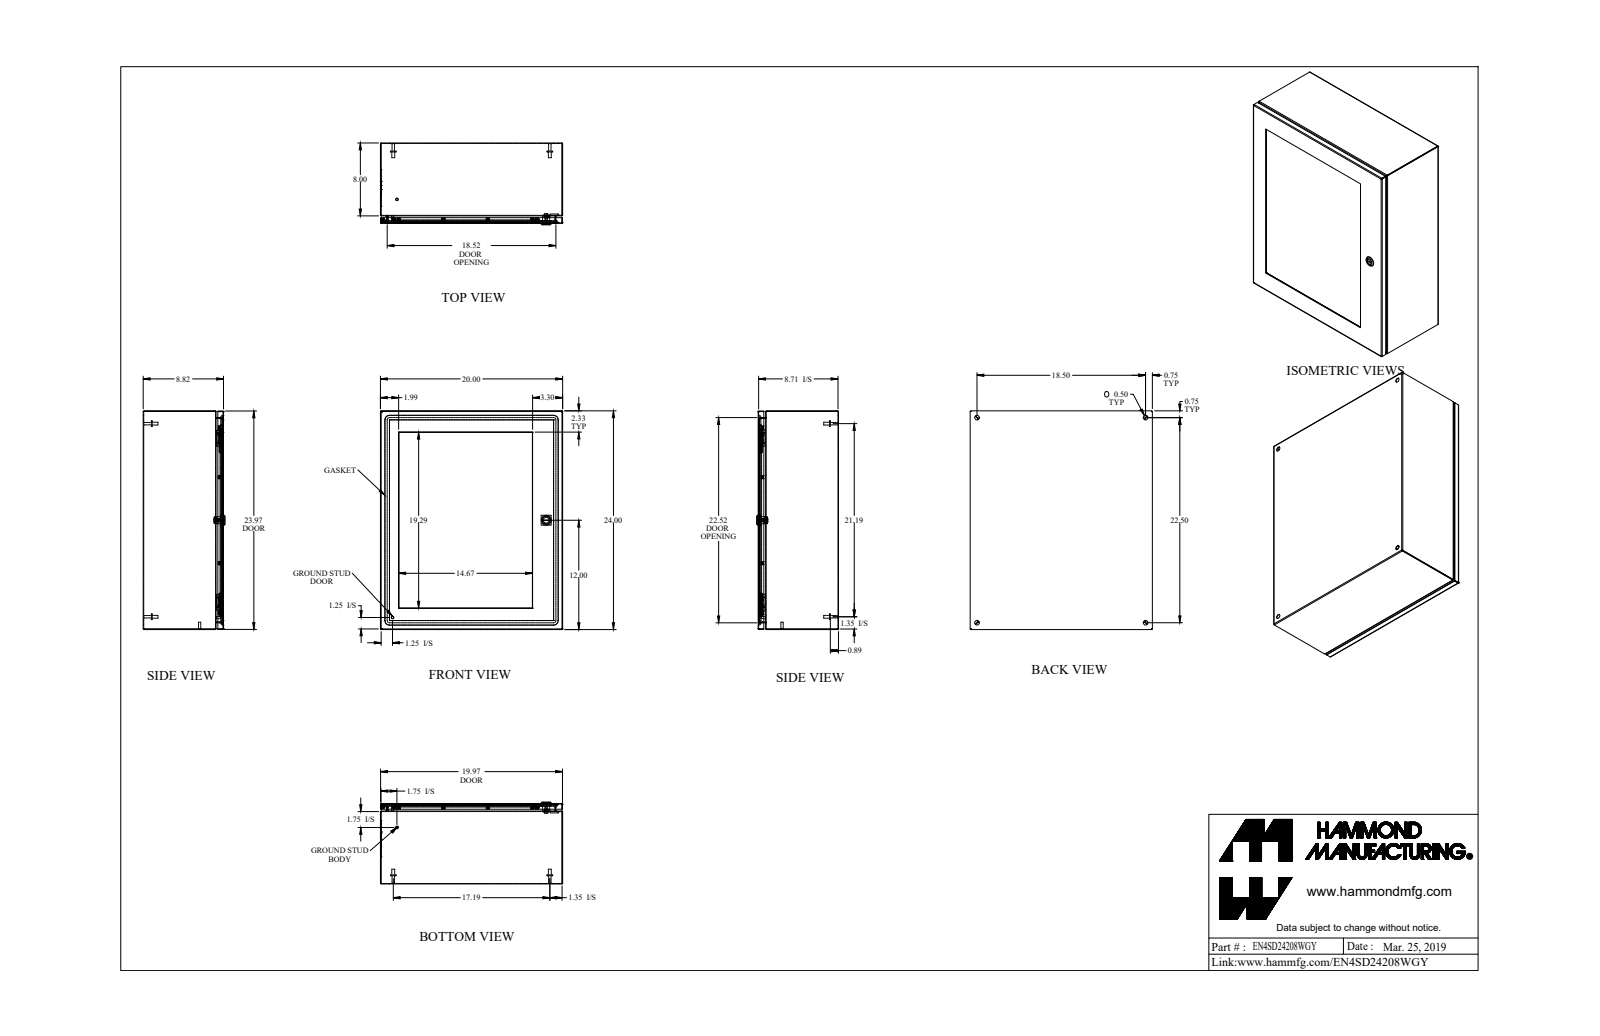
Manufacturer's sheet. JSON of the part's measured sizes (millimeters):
{"part_name": "EN4SD24208WGY_Default", "step_written_by": "SolidWorks 2019 (CONFIG_CONTROL_DESIGN)", "units": "millimeters", "bodies": {"solids": 66, "faces": 1333, "planar": 662, "cylindrical": 409, "other": 262}, "overall_size": [609.6, 508, 228.1], "volume_mm3": 2932000, "surface_area_mm2": 2675000, "round_holes": [[3.3, 18], [6.4, 18], [12.7, 4], [4.4, 1], [5.9, 1], [6.1, 1], [6.1, 1], [15.9, 1], [19.9, 1]], "round_bosses_or_shafts": [[5.7, 19], [9.3, 18], [4.2, 18], [15.9, 4], [8, 4], [6.9, 4], [7.1, 2], [6.4, 2]], "partial_cylinders_radius": [[0.7, 21], [2.2, 21], [6.4, 16], [3.2, 10], [482.6, 8], [0.2, 4], [0.4, 4], [1.6, 4]], "face_to_face_distances": [1.4, 222.6, 221.2, 506.6, 6.4, 214.8, 216.3, 608.2, 505.1, 508], "hole_center_spacings": [119.9, 124.2, 124.2, 248.4, 262.2, 416.6, 465.4, 516.5]}
